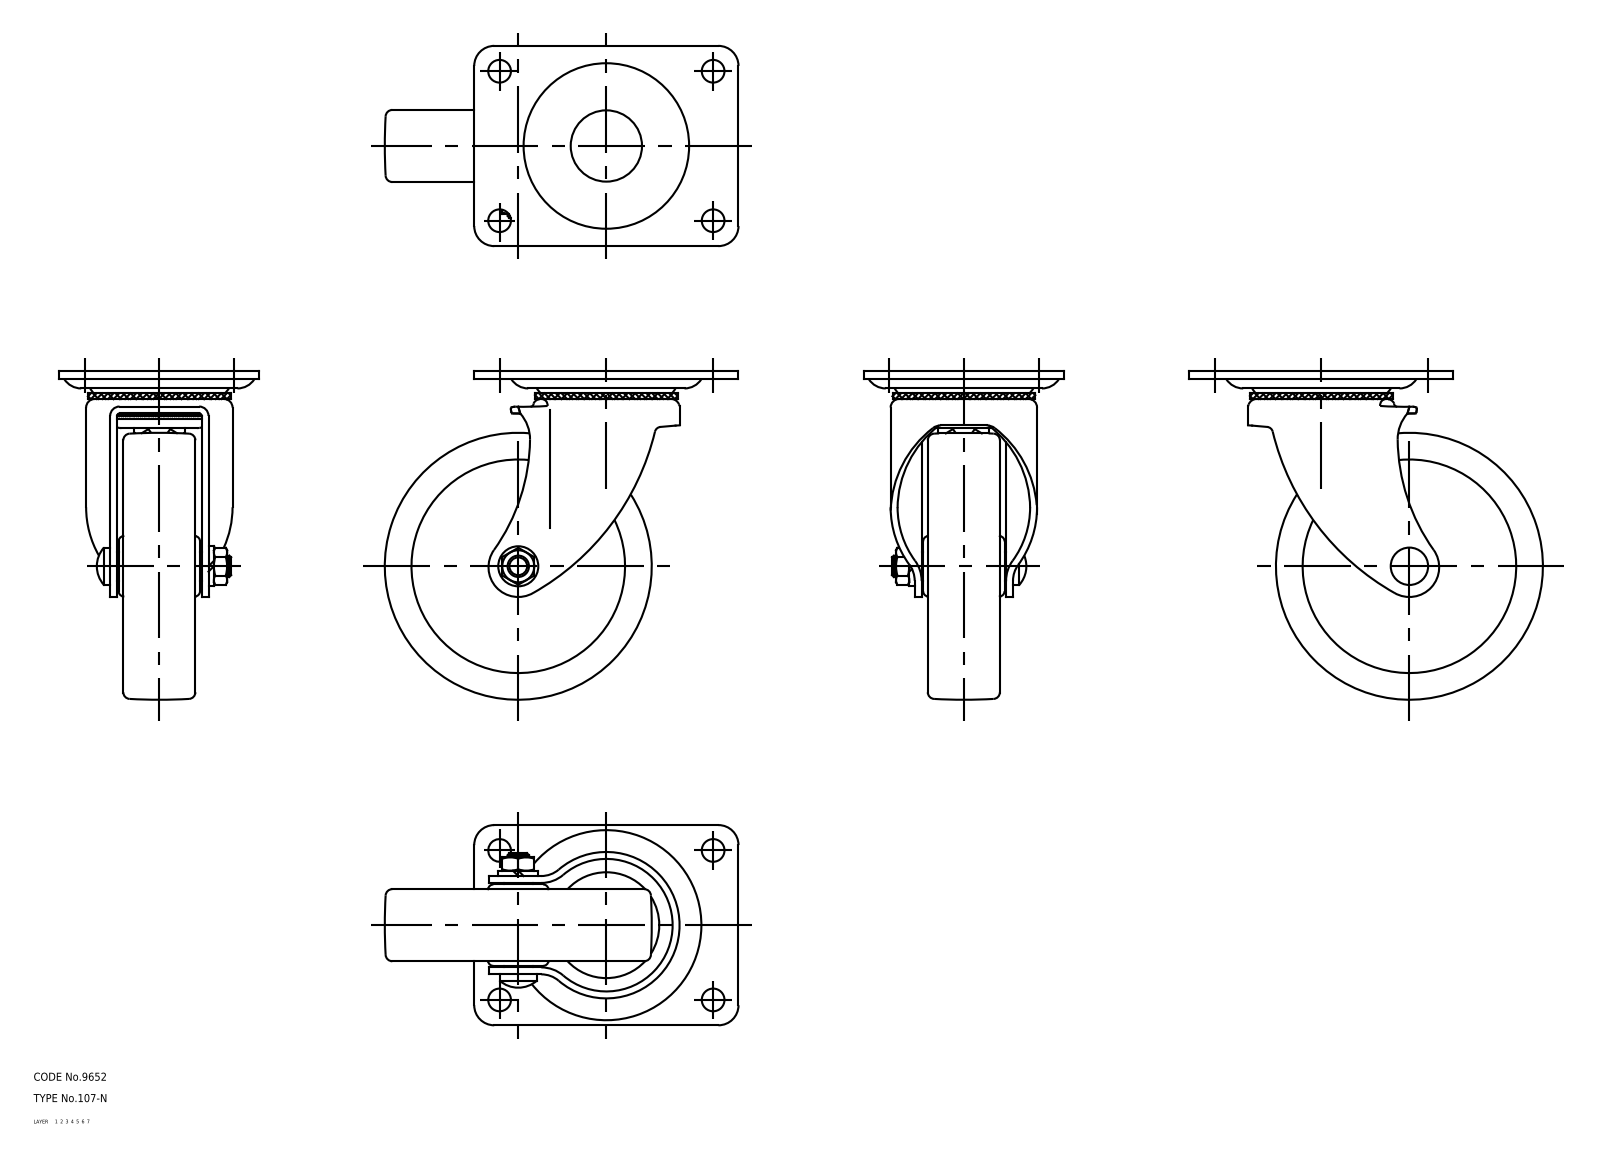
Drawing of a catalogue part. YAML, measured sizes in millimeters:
part_name: "wheel; mounting plate; main shaft; axle (+1 more)"
step_written_by: "CADfix (AUTOMOTIVE_DESIGN)"
units: millimeters
bodies: {solids: 5, faces: 217, planar: 0, cylindrical: 0, other: 217}
overall_size: [132.5, 123, 75]
volume: 207625
surface_area: 70698
